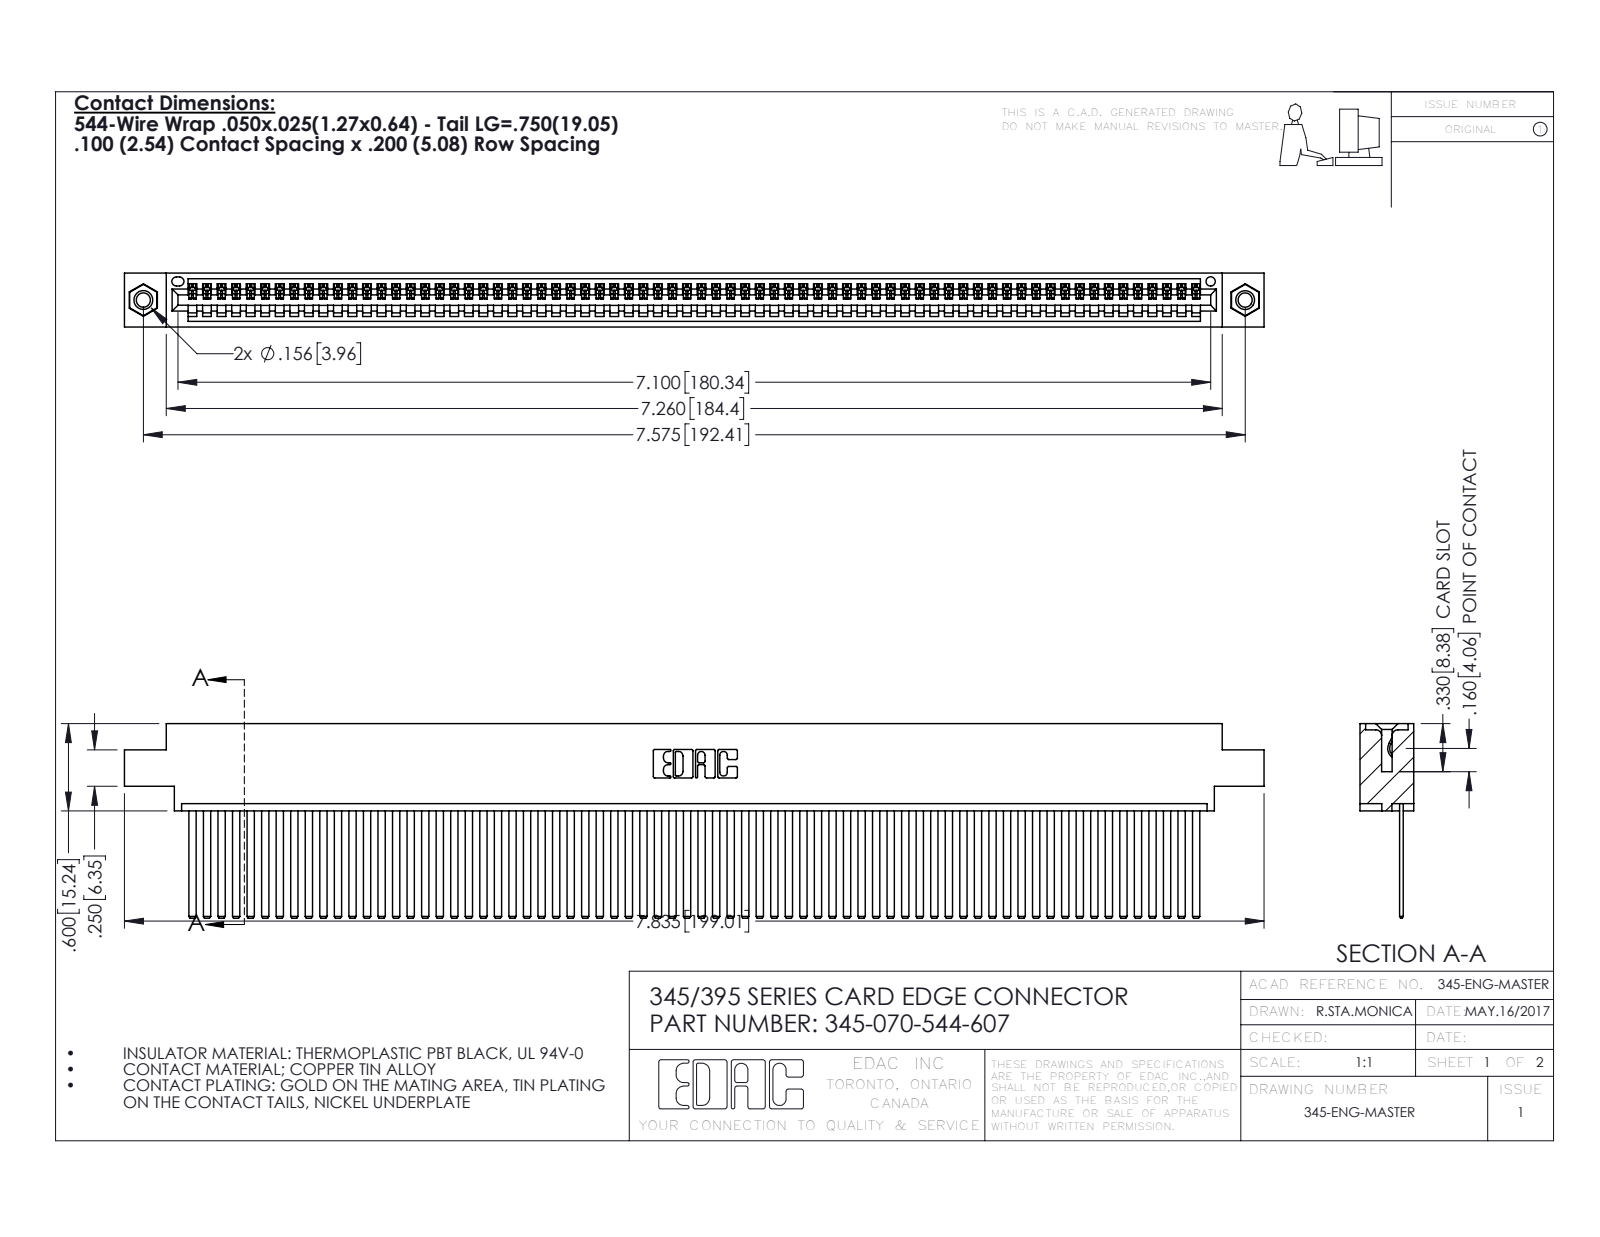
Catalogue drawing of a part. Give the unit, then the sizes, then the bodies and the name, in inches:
Units: inches
Overall size (bounding box): 7.835 × 1.337 × 0.37
Round holes (diameter × count): ⌀0.098 ×2, ⌀0.125 ×2, ⌀0.156 ×2, ⌀0.064 ×1
Round bosses / shafts (diameter × count): ⌀0.155 ×2
Partial cylindrical surfaces — rounded edges, fillets, slot ends (radius × count): R0.006 ×140, R0.01 ×22, R0.007 ×6, R0.031 ×6, R0.026 ×3, R0.031 ×2, R0.04 ×2, R0.014 ×1
Main face-to-face distances: 0.072, 0.298, 0.025, 0.098, 0.272, 0.37, 0.2, 0.225, 0.175, 0.149
Hole centre spacings: 0.27, 7.339, 7.575
Volume: 1.209 in³ · Surface area: 45.42 in²
Bodies: 73 solids, 3830 faces (2636 planar, 1178 cylindrical, 16 other)
Part name (STEP PRODUCT): 345-250-001_345-250-005-103; 345-070-544-607; 345-292-001_345-293-144; 345 Part_0.170 Offset - 0.156 Dia-TI
STEP written by: SolidWorks 2016 (CONFIG_CONTROL_DESIGN)
